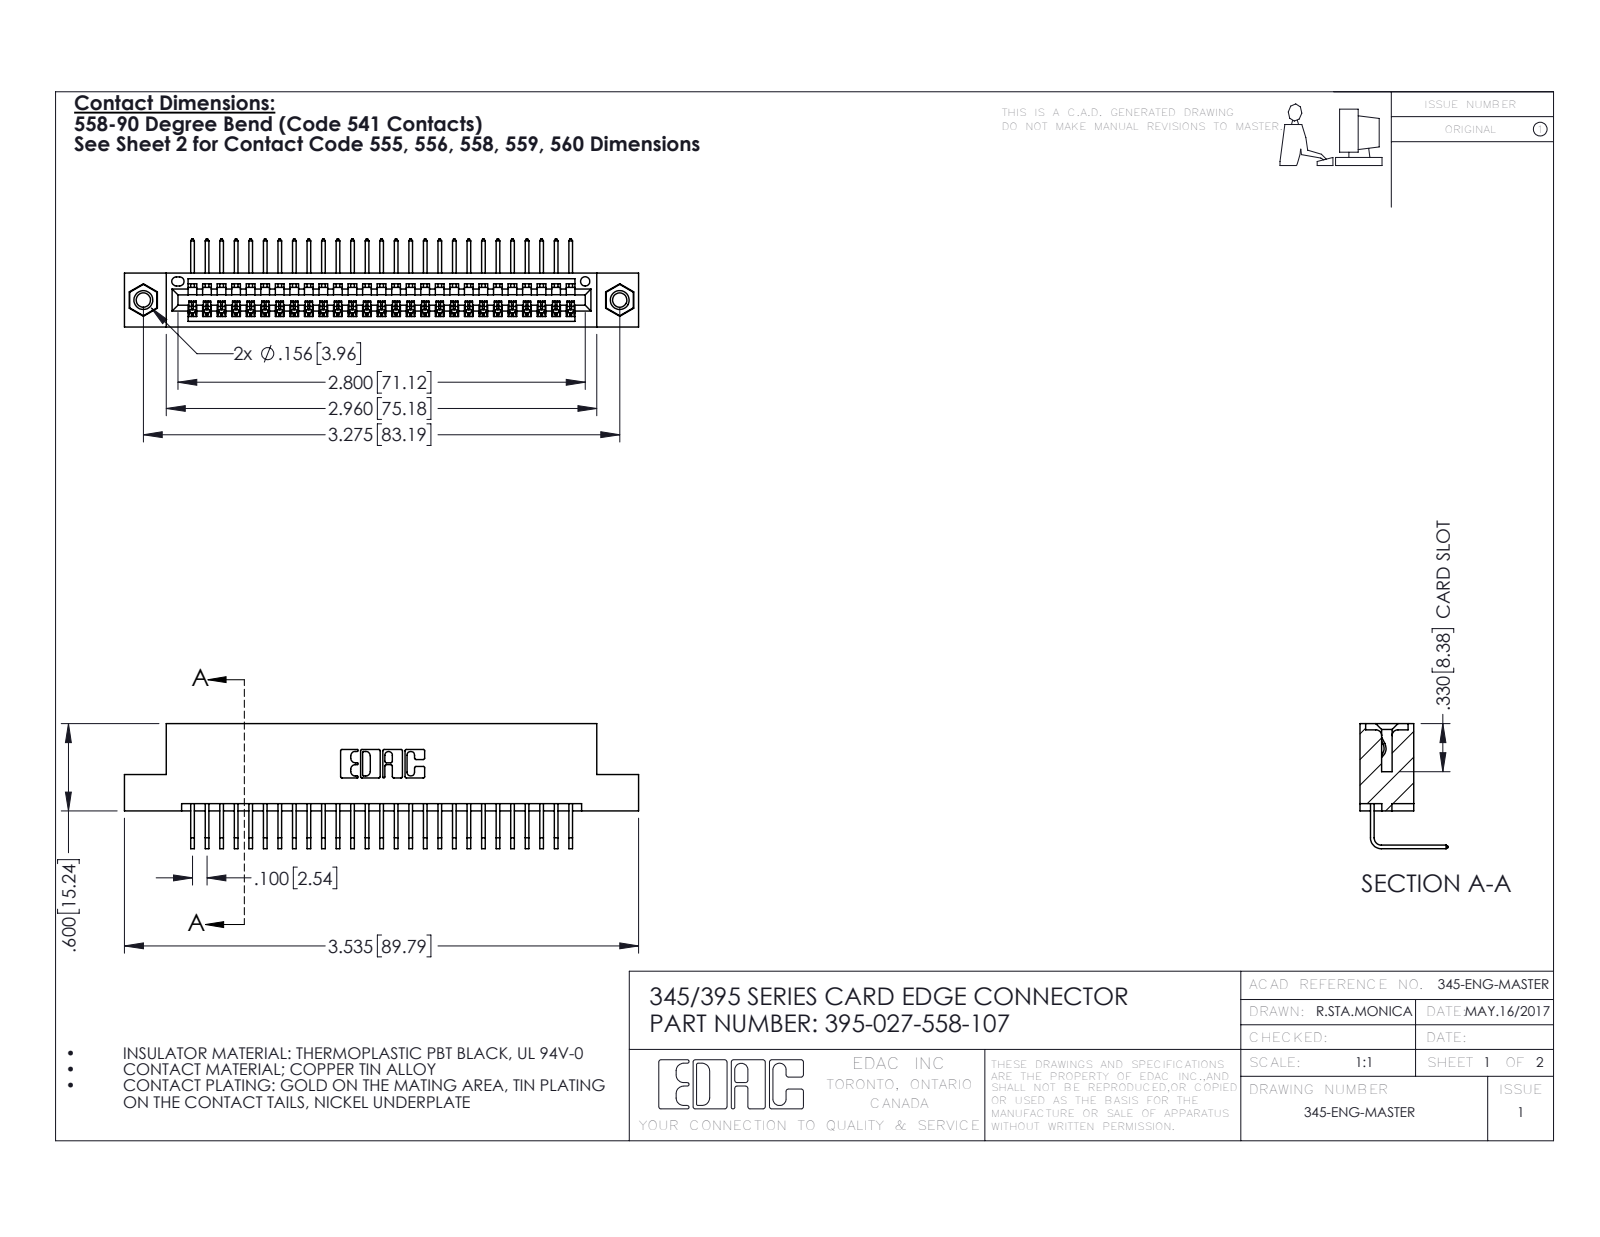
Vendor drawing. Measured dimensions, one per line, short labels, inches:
name: 395-027-558-107; 345 Part_Flush Mounting Lugs - 0.156 Dia-TI; 345-250-001_345-250-005-103; 345-292-001_558 Tail - 2
written by: SolidWorks 2016 (CONFIG_CONTROL_DESIGN)
unit: in
bodies: 30 solids, 1806 faces (1246 planar, 544 cylindrical, 16 other)
size: 3.535 × 0.859 × 0.605
volume: 0.518 in³; area: 18.02 in²
holes: 2× ⌀0.098, 2× ⌀0.125, 2× ⌀0.156, 1× ⌀0.064
bosses: 2× ⌀0.155
rounds: 54× R0.006, 22× R0.01, 6× R0.007, 6× R0.031, 3× R0.026, 2× R0.031, 2× R0.04, 1× R0.014
face distances: 0.072, 0.298, 0.2, 0.37, 0.098, 0.272, 0.025, 0.225, 0.149, 0.072
hole spacings: 0.27, 3.04, 3.275
